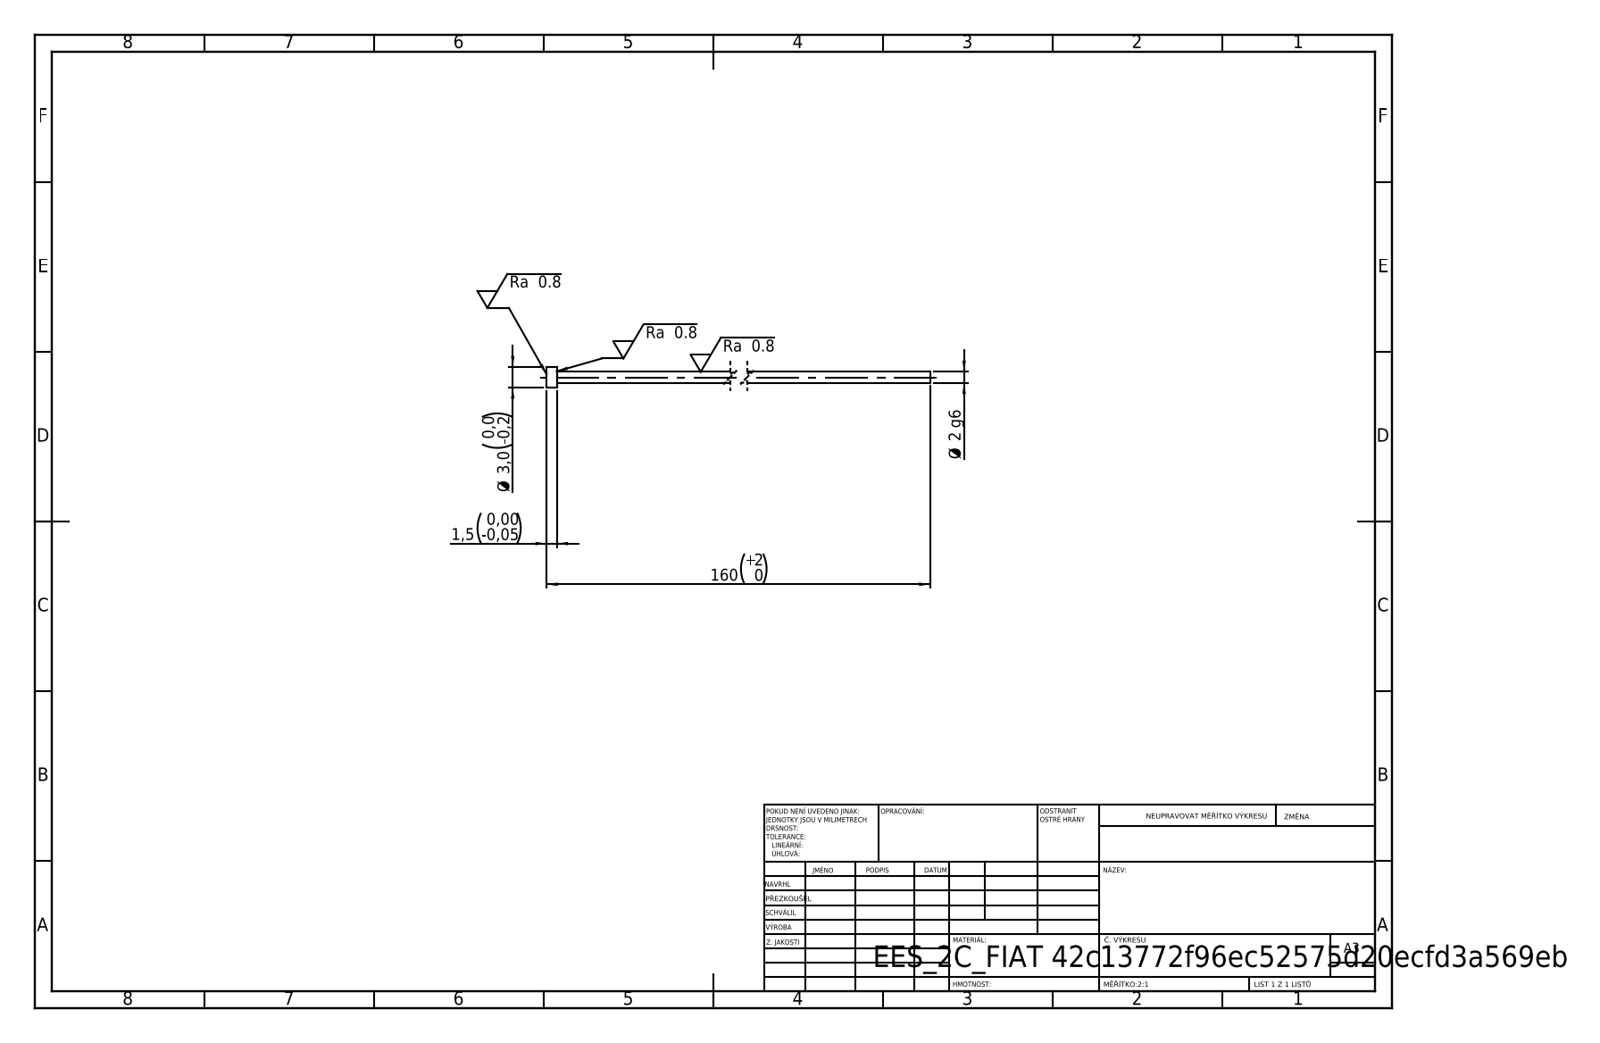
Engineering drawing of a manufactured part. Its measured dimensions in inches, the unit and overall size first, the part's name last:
Units: inches
Overall size (bounding box): 6.299 × 0.118 × 0.118
Round bosses / shafts (diameter × count): ⌀0.118 ×1, ⌀0.063 ×1
Main face-to-face distances: 0.059, 6.299, 6.24
Volume: 0.02 in³ · Surface area: 1.28 in²
Bodies: 1 solid, 7 faces (3 planar, 4 cylindrical, 0 other)
STEP written by: SolidWorks 2019 (CONFIG_CONTROL_DESIGN)
